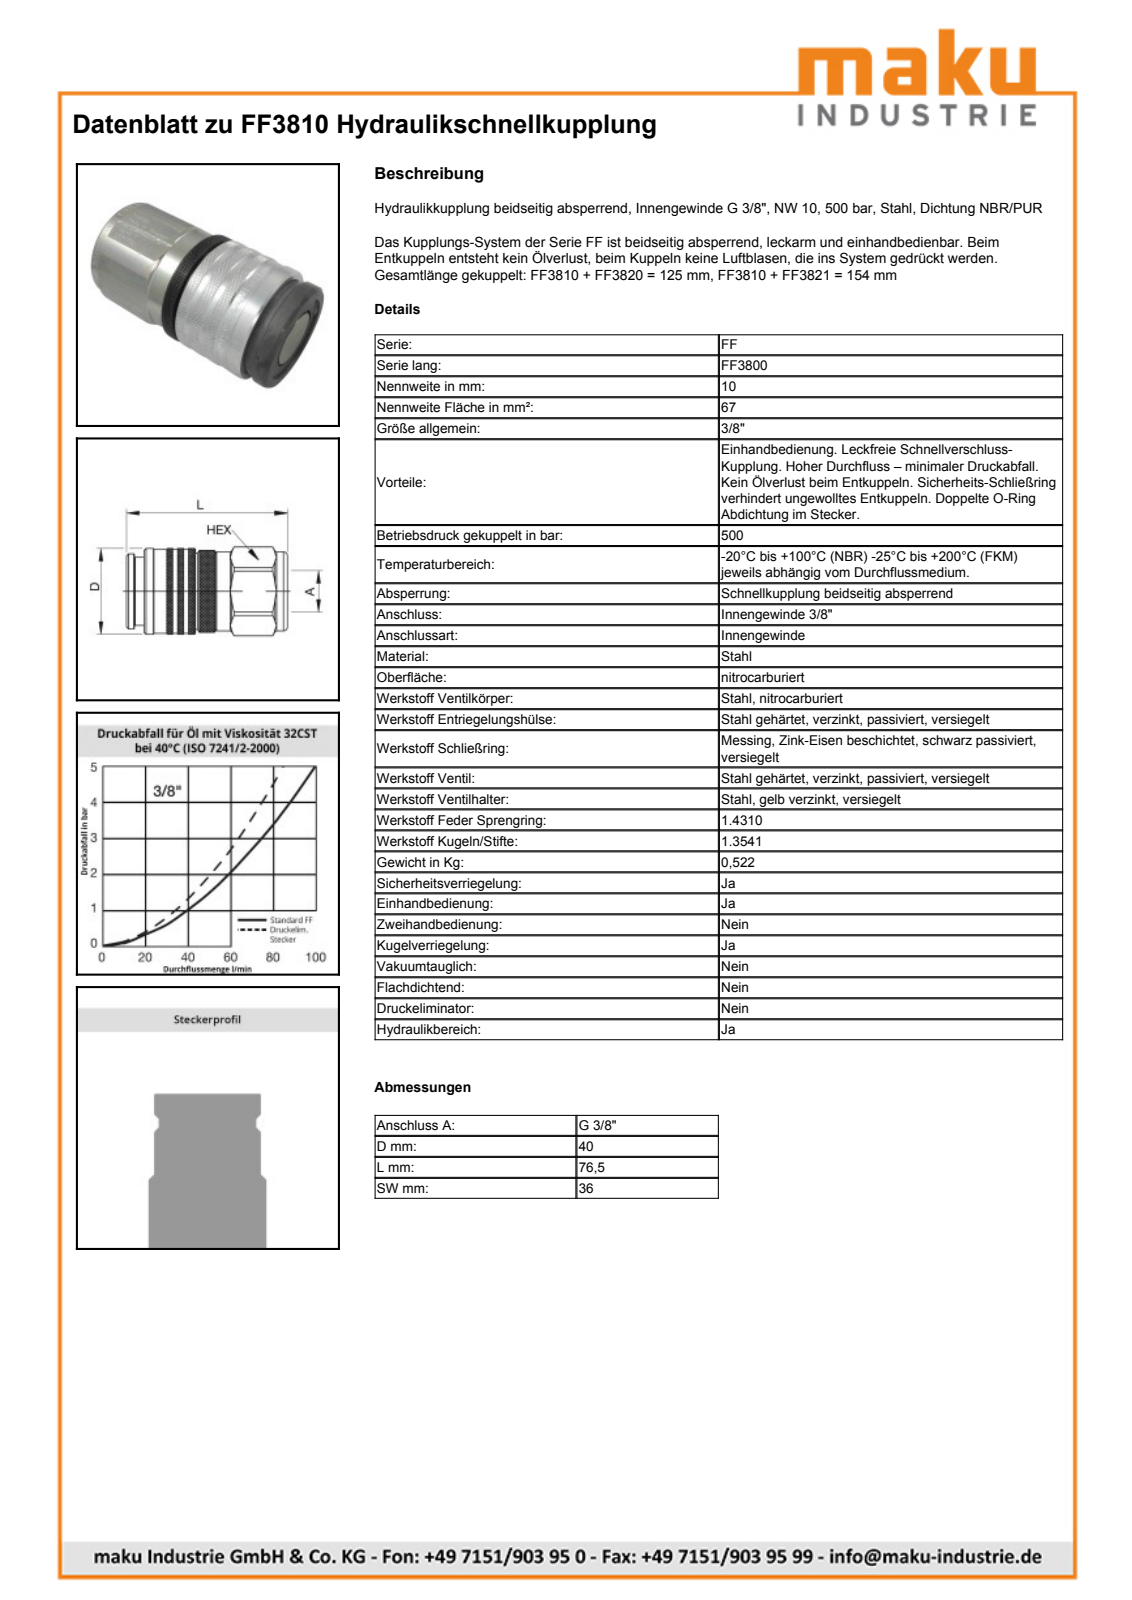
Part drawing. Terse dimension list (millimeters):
name: FF3810
written by: SolidWorks 2009 (AUTOMOTIVE_DESIGN)
unit: mm
bodies: 1 solid, 134 faces (24 planar, 46 cylindrical, 64 other)
size: 76.5 × 40 × 40
volume: 82 722 mm³; area: 13 816 mm²
holes: 1× ⌀13.1, 1× ⌀14.95, 1× ⌀15.1, 1× ⌀26.5, 1× ⌀32.2, 1× ⌀36.5
bosses: 1× ⌀40, 1× ⌀39, 1× ⌀38.7, 1× ⌀36, 1× ⌀35, 1× ⌀32, 1× ⌀13
face distances: 36, 74.95, 69.6, 5.35, 76.5, 6.9, 1.55, 32.5, 37.1, 42.45
